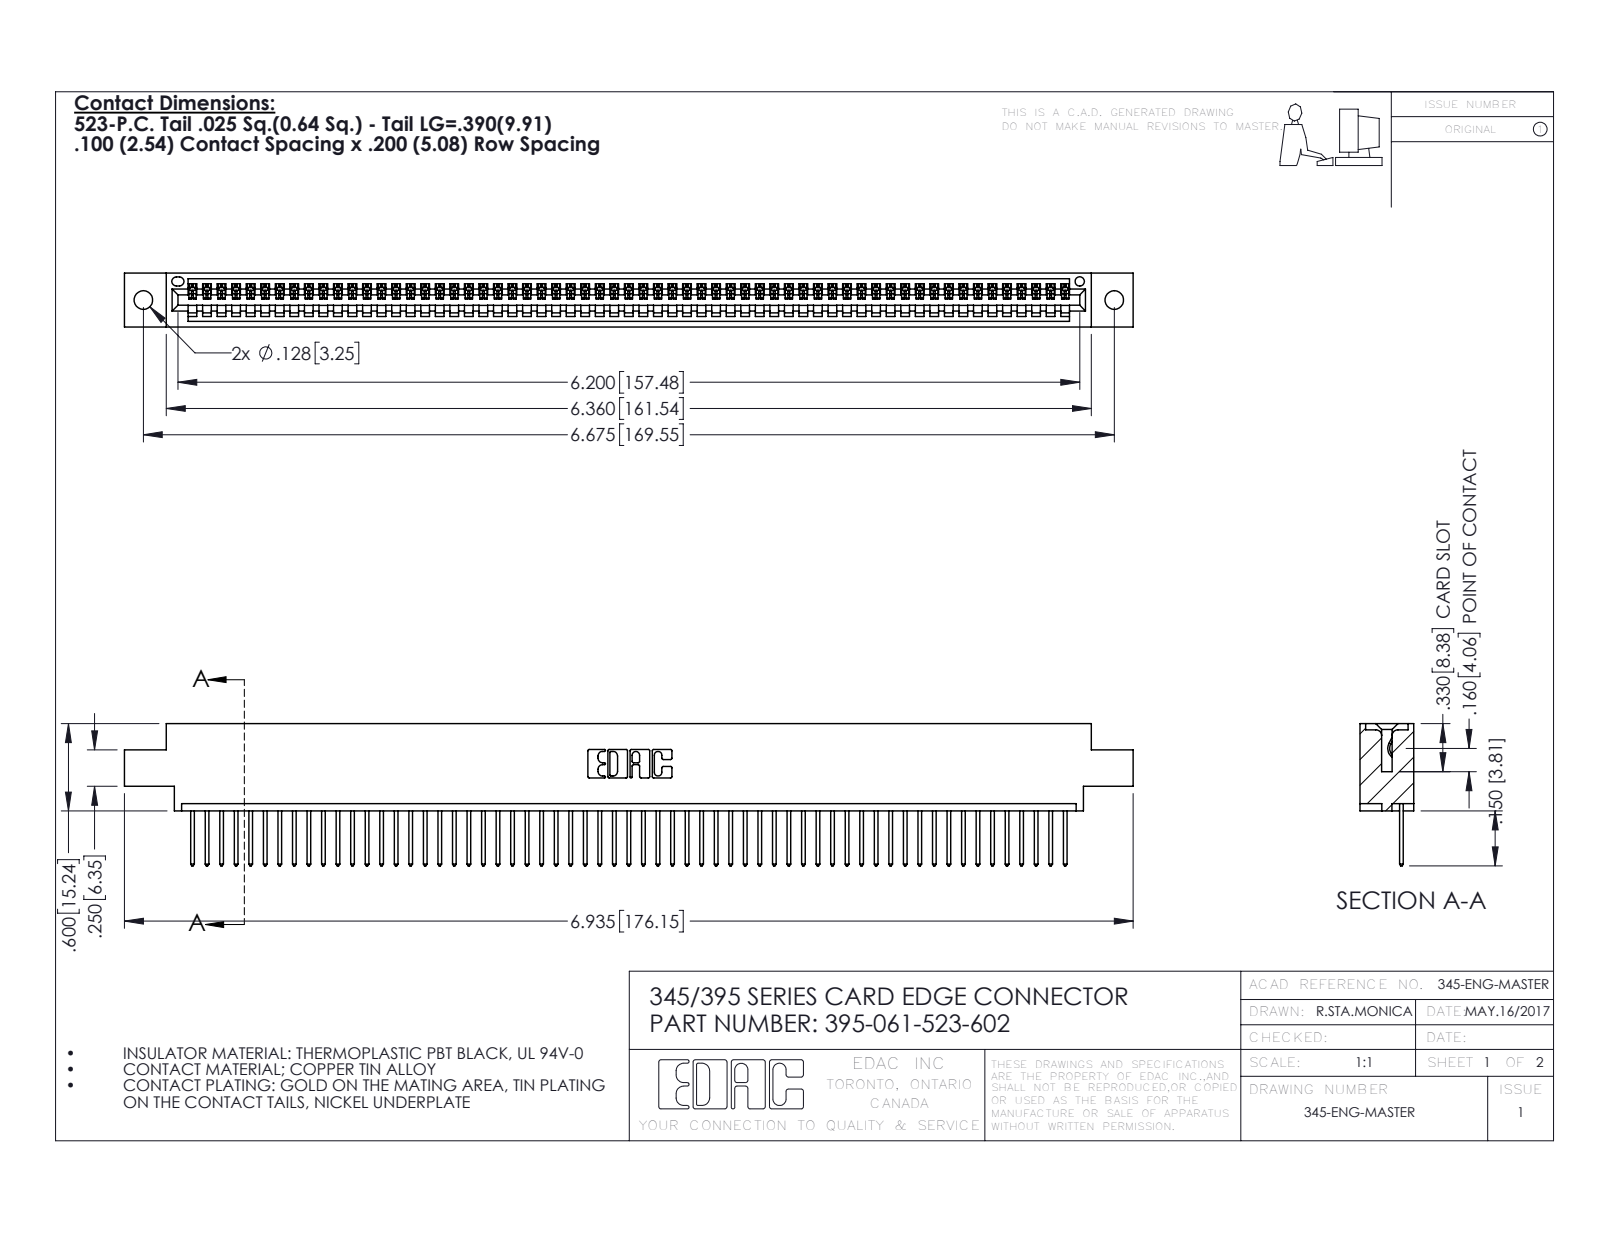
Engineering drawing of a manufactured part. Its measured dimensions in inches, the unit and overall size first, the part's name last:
Units: inches
Overall size (bounding box): 6.935 × 0.977 × 0.37
Round holes (diameter × count): ⌀0.128 ×2, ⌀0.064 ×1
Partial cylindrical surfaces — rounded edges, fillets, slot ends (radius × count): R0.006 ×122, R0.01 ×122, R0.01 ×22, R0.007 ×6, R0.031 ×6, R0.026 ×3, R0.031 ×2, R0.04 ×2
Main face-to-face distances: 0.298, 0.072, 0.37, 0.098, 0.272, 0.025, 0.2, 0.225, 0.175, 0.149
Hole centre spacings: 0.27, 6.439, 6.675
Volume: 1.02 in³ · Surface area: 34.7 in²
Bodies: 62 solids, 3668 faces (2524 planar, 1144 cylindrical, 0 other)
Part name (STEP PRODUCT): 345-292-001_345-293-123; 395-061-523-602; 345 Part_0.170 Offset - 0.128 Dia
STEP written by: SolidWorks 2016 (CONFIG_CONTROL_DESIGN)
